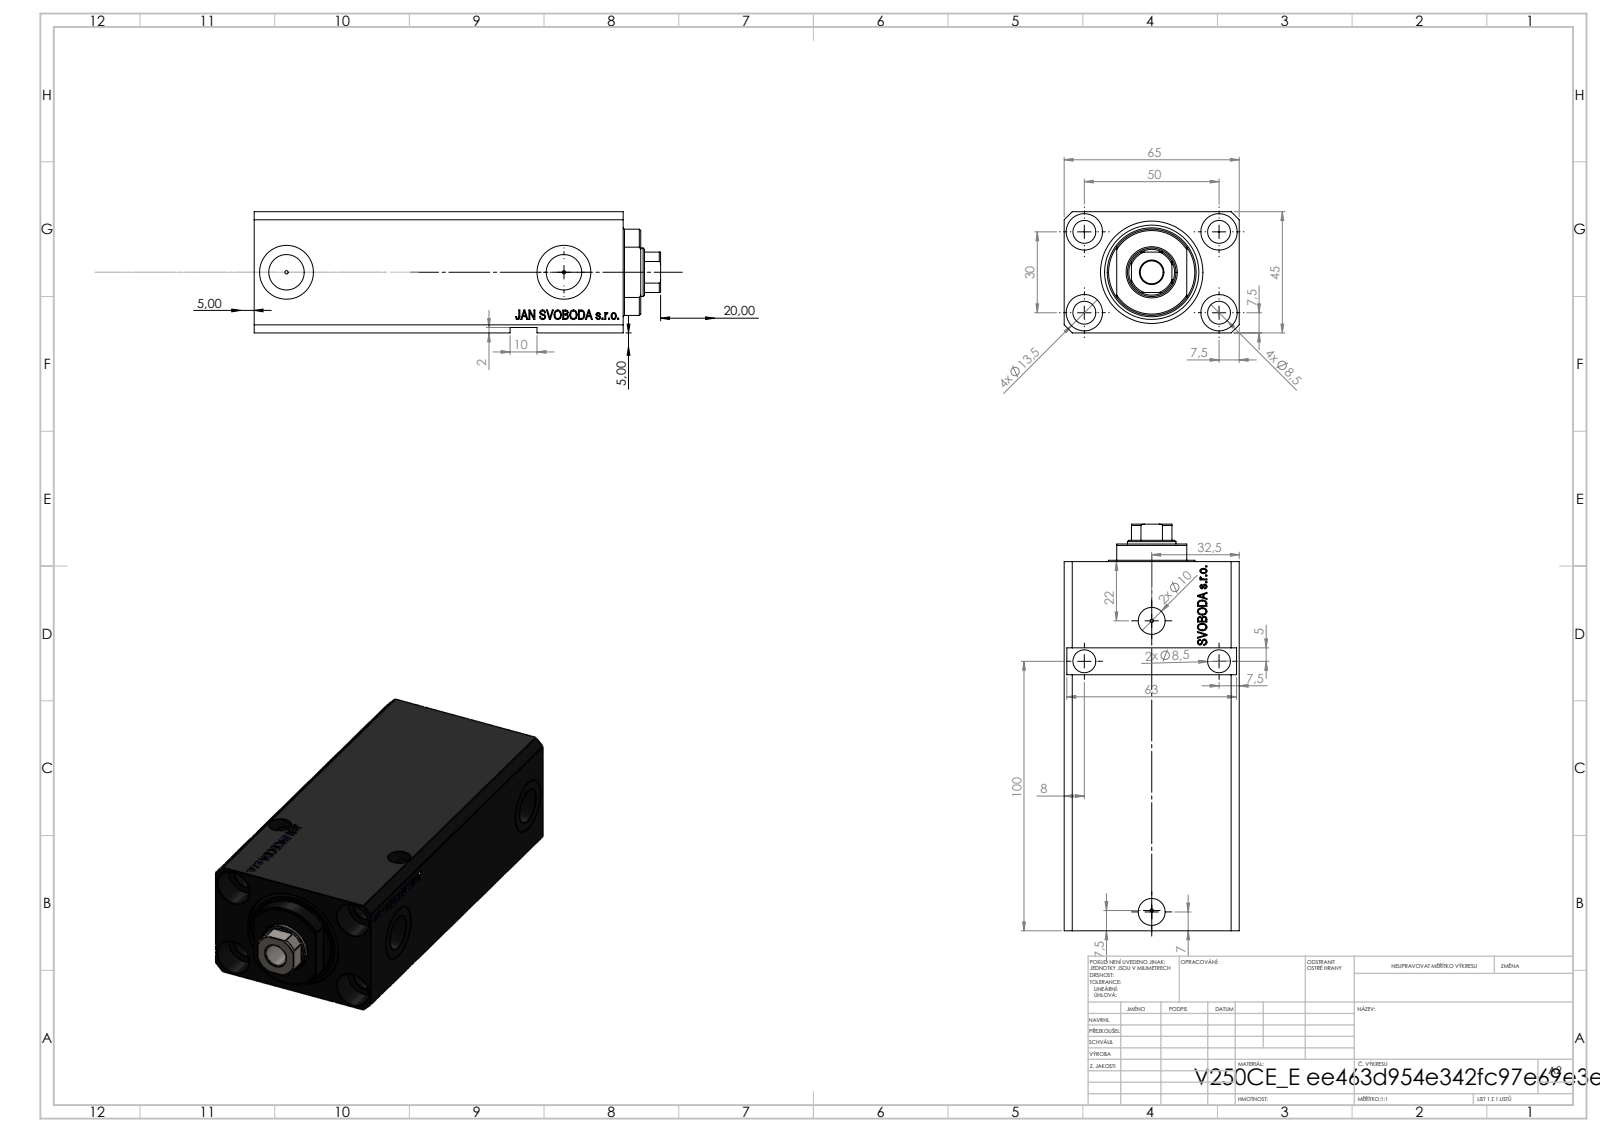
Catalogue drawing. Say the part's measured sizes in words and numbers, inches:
The part is named "V250CE_VC_E; V250CE_C_VCP; V250CE_E_Body". Its 3-D file was written by "SolidWorks 2019 (CONFIG_CONTROL_DESIGN)". It is 3 solids with 933 faces: 439 planar, 116 cylindrical and 378 other. Overall it measures 5.945 by 2.559 by 1.772 inches. Its volume is 20.21 cubic inches and its surface area 126.6 square inches. Round holes: 9 of diameter 0.335, 4 of diameter 0.049, 4 of diameter 0.531, 2 of diameter 0.394, 2 of diameter 0.518, 2 of diameter 0.787, 1 of diameter 0.709, 1 of diameter 0.984, 1 of diameter 1.496. Partial cylindrical surfaces (rounded edges, fillets, slot ends): 1 of radius 0.335, 1 of radius 0.63. The main face-to-face distances are 1.772, 2.559, 4.843, 0.551, 5.394, 0.272, 4.571, 5.122, 1.693, 2.555. The hole center spacings are 1.148, 1.969, 1.181, 1.323, 1.337, 2.296, 2.756, 3.387.
